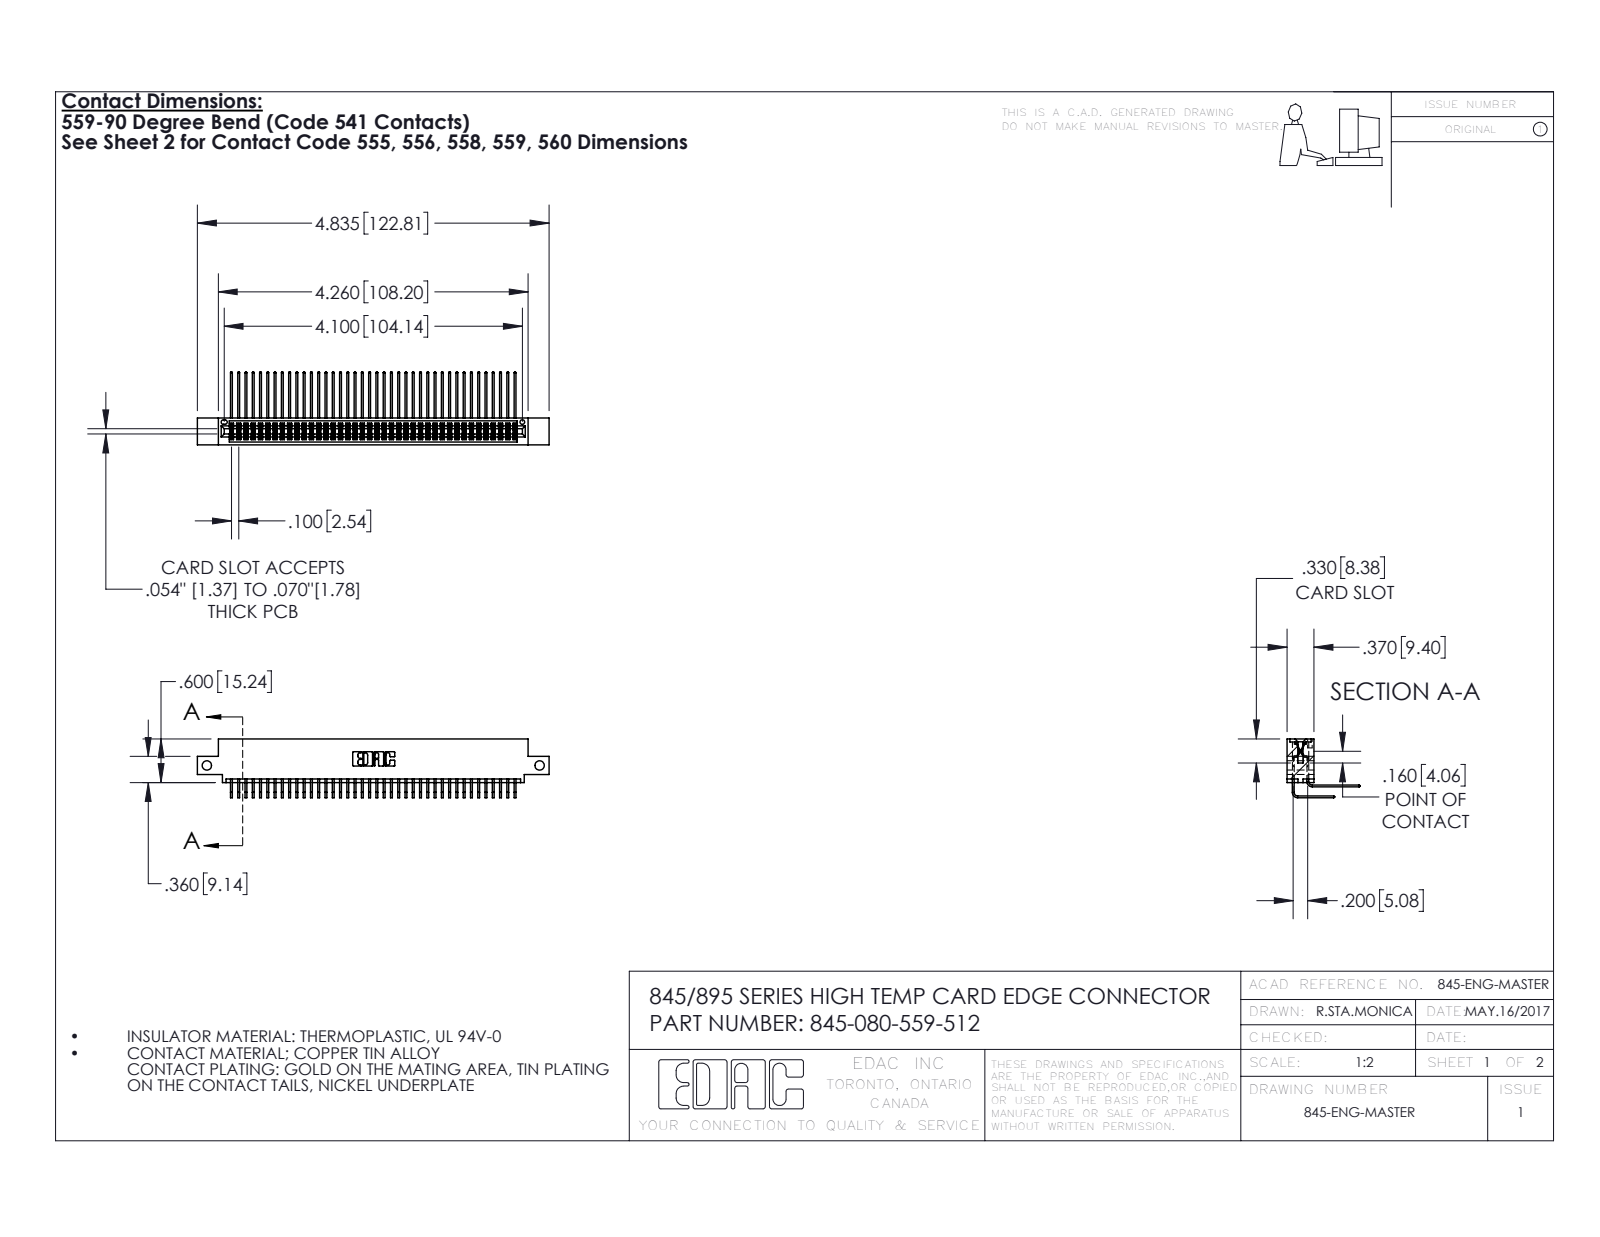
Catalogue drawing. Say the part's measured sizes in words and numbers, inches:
The part is named "345-292-001_558 559 Tail - 1; 345 Part_0.110 Offset - Side Mount; 345-080-559-512; 345-292-001_559 Tail - 2". Its 3-D file was written by "SolidWorks 2016 (CONFIG_CONTROL_DESIGN)". It is 81 solids with 4290 faces: 2884 planar, 1406 cylindrical and 0 other. Overall it measures 4.835 by 1.005 by 0.809 inches. Its volume is 0.745 cubic inches and its surface area 31.22 square inches. Round holes: 2 of diameter 0.128, 1 of diameter 0.064. Partial cylindrical surfaces (rounded edges, fillets, slot ends): 120 of radius 0.006, 22 of radius 0.01, 6 of radius 0.007, 6 of radius 0.031, 3 of radius 0.026, 2 of radius 0.014, 2 of radius 0.019, 2 of radius 0.022. The main face-to-face distances are 0.072, 0.298, 0.2, 0.37, 0.098, 0.272, 0.025, 0.225, 0.175, 0.15. The hole center spacings are 4.575.
